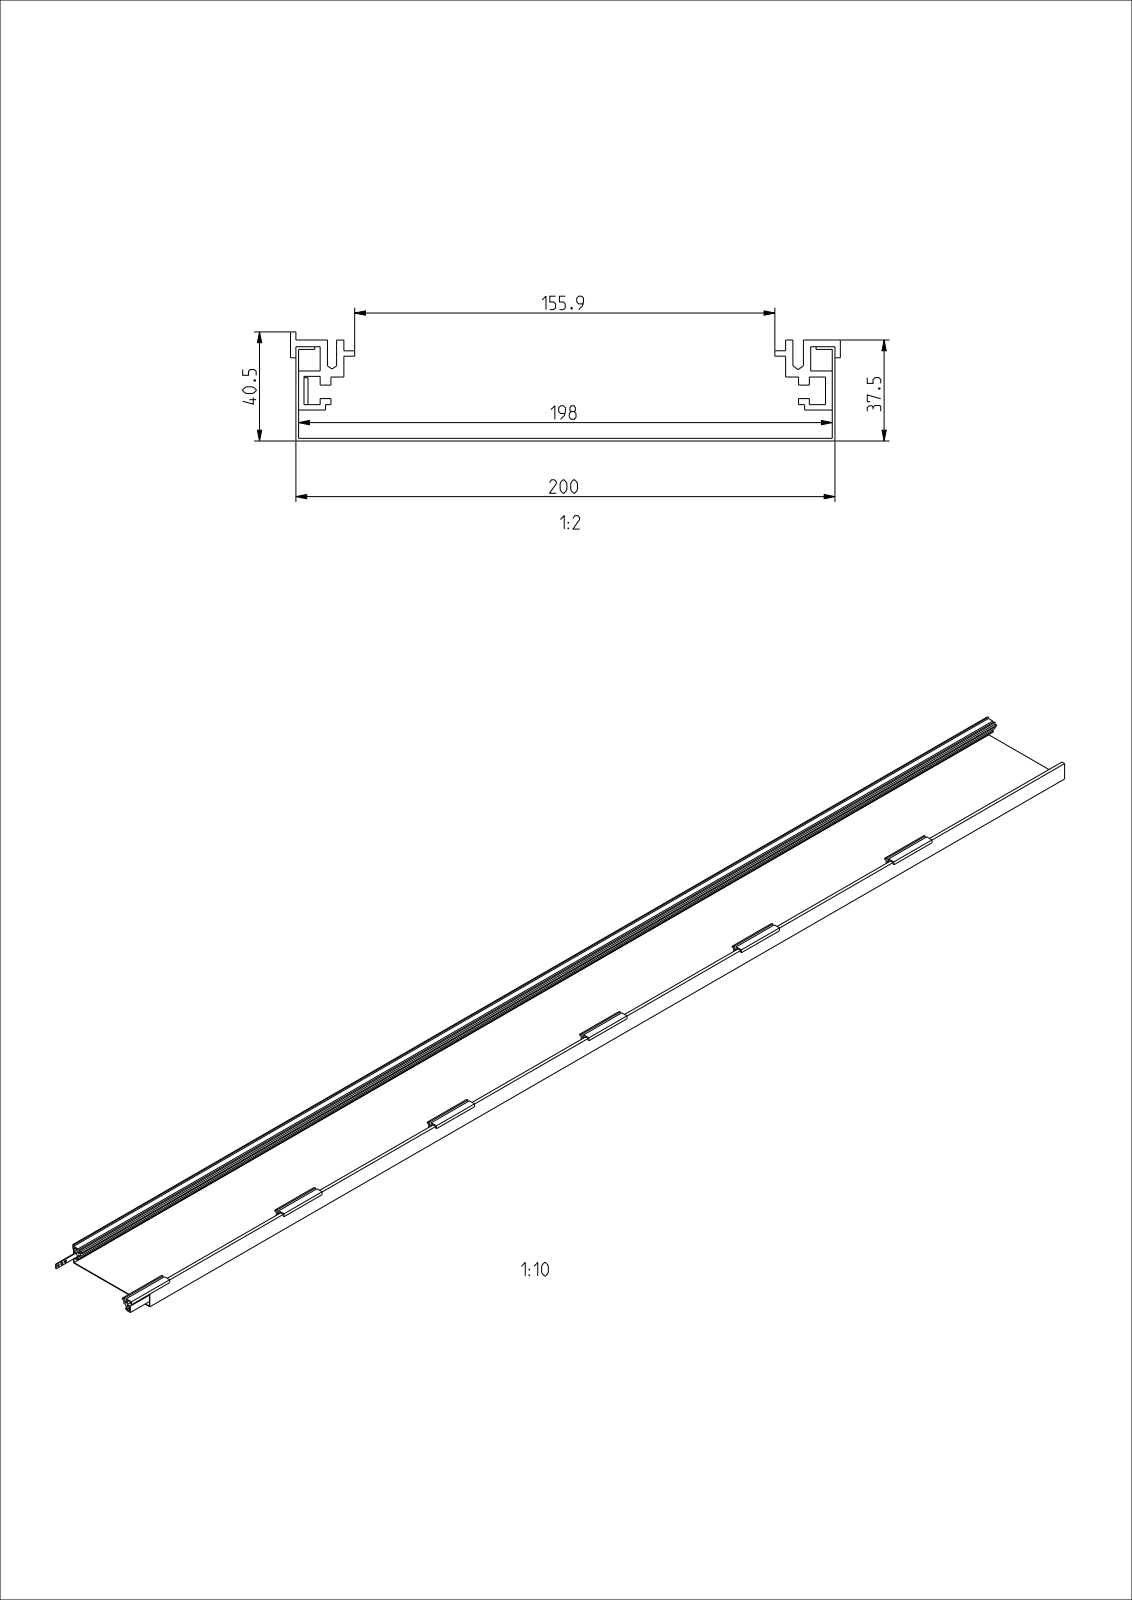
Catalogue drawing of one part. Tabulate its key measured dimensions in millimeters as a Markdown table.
| quantity | value |
| --- | --- |
| part name | AKU2000401_WANNE_3; AKU_SEITENPROFIL_APA_K24_6; ZES_VK180_KUN_3; AKU_SEITENPROFIL_APA_O01_4 (+1 more) |
| STEP written by | CREO PARAMETRIC BY PTC INC, 2022281 (AUTOMOTIVE_DESIGN) |
| units | millimeters |
| bodies | 9 solids, 265 faces (253 planar, 12 cylindrical, 0 other) |
| overall size | 2450 × 204 × 40.5 |
| volume | 1 317 000 mm³ |
| surface area | 1 893 000 mm² |
| round holes (diameter × count) | 5.5 × 4, 4.2 × 2 |
| main face-to-face distances | 1, 199, 2, 34, 198, 200, 8, 3, 9, 12.5 |
| hole center spacings | 9.25, 66.5, 18.5, 57.25, 75.75, 48, 85 |
